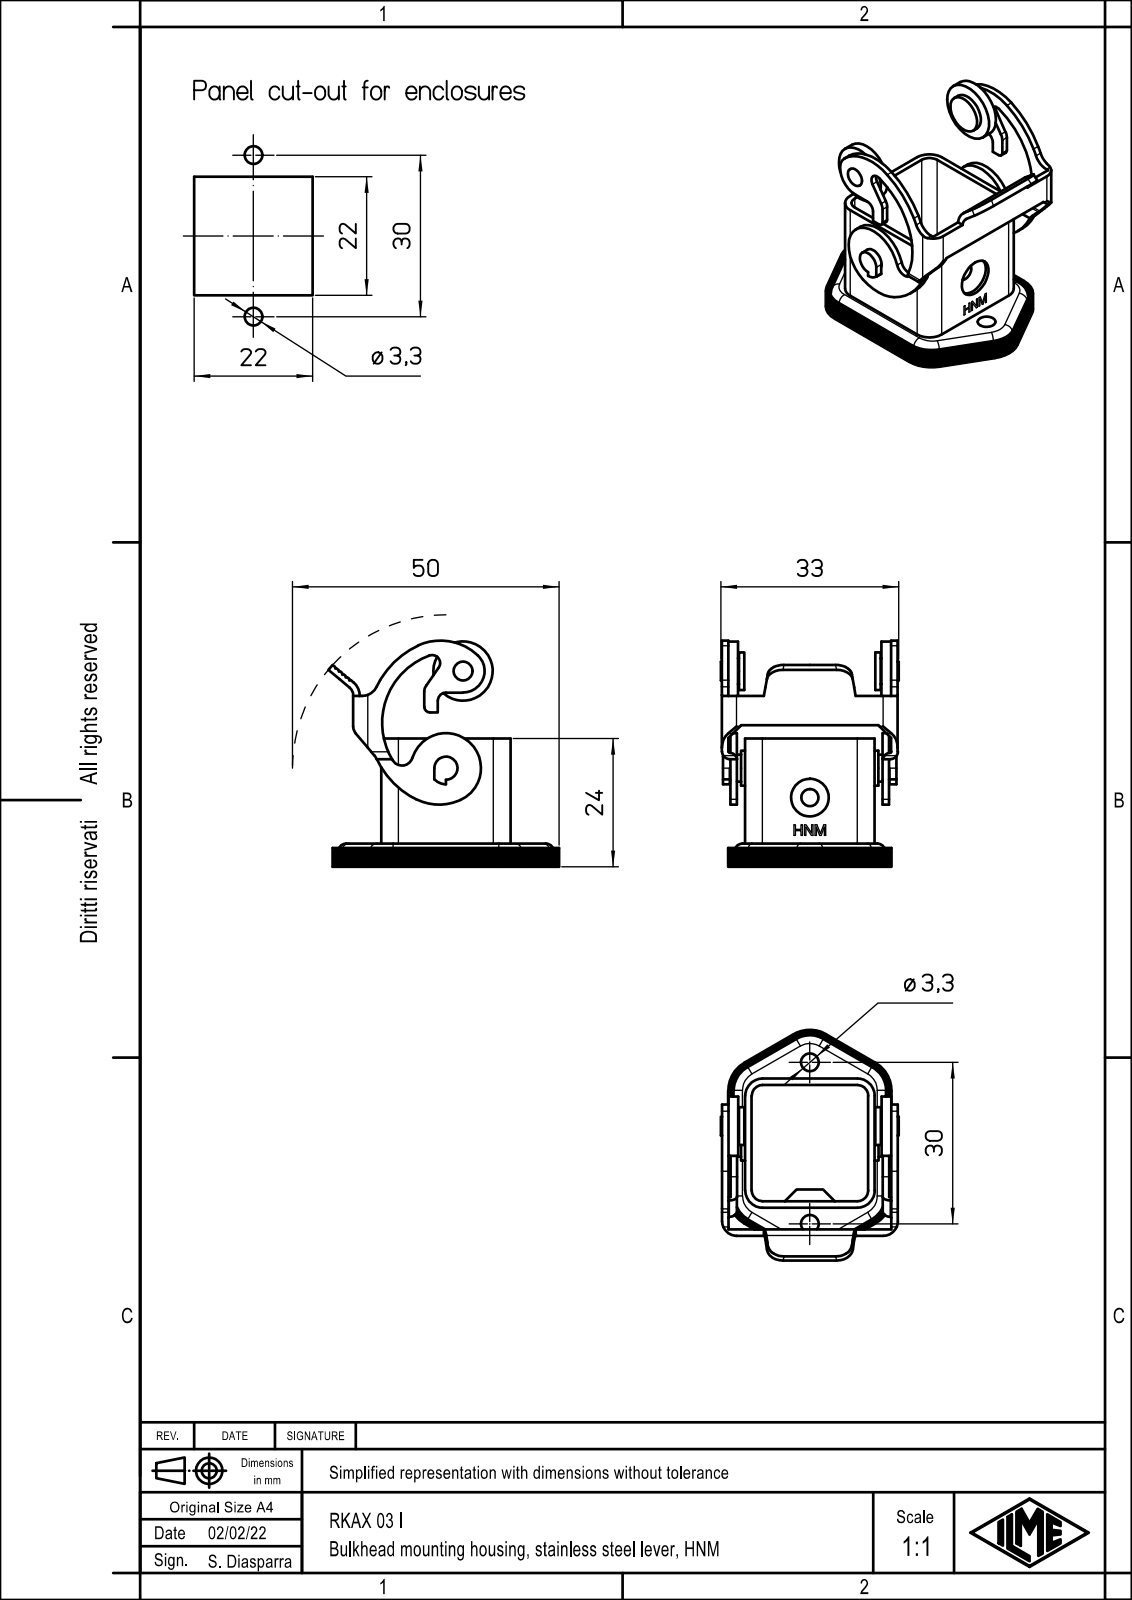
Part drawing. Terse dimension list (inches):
name: RKAX_03_I
written by: Creo Elements/Direct Modeling 20.1B 02-Apr-2019 (C) Parametric Technology GmbH (AUTOMOTIVE_DESIGN)
unit: in
bodies: 1 solid, 308 faces (156 planar, 143 cylindrical, 9 other)
size: 1.685 × 1.652 × 1.299
volume: 0.379 in³; area: 13.45 in²
holes: 2× ⌀0.114, 2× ⌀0.13, 1× ⌀0.126, 1× ⌀0.276
bosses: 1× ⌀0.433, 1× ⌀0.276, 1× ⌀0.256, 1× ⌀0.197, 1× ⌀0.189, 1× ⌀0.169, 1× ⌀0.138
rounds: 15× R0.01, 12× R0.079, 12× R0.197, 8× R0.059, 6× R0.236, 5× R0.118, 5× R0.126, 4× R0.055
face distances: 0.047, 0.898, 0.85, 0.945, 1.102, 0.205, 1.005, 0.107, 0.106, 1.004
hole spacings: 1.181
